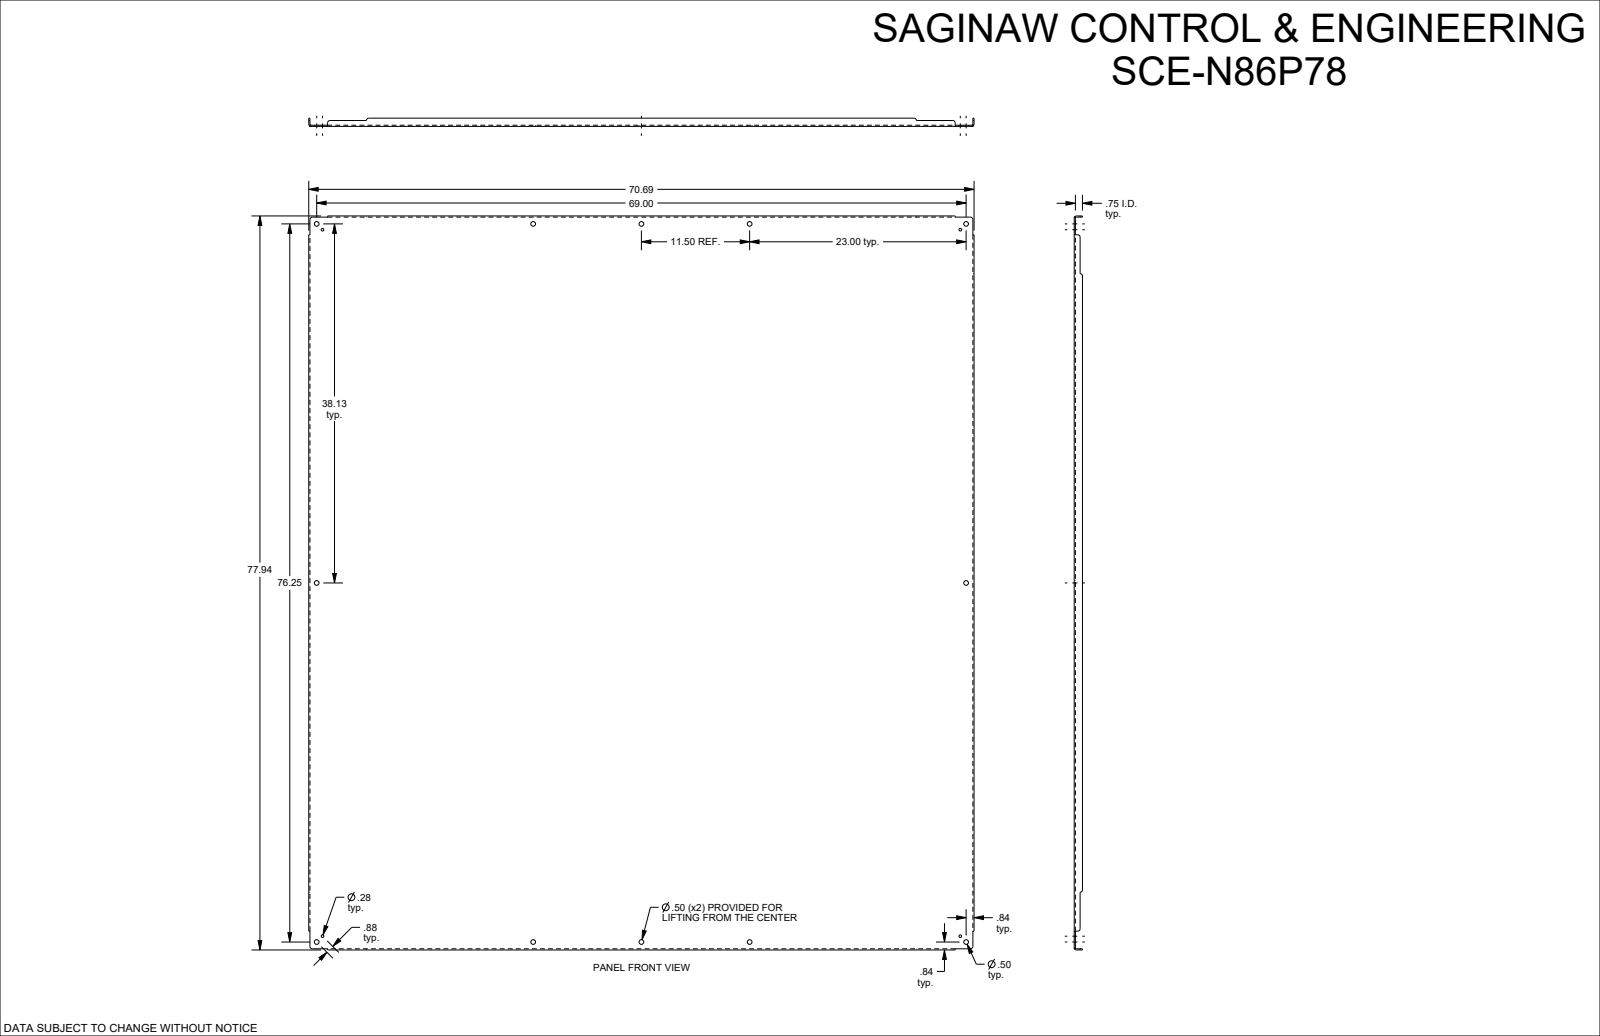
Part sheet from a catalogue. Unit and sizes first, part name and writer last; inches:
Units: inches
Overall size (bounding box): 77.938 × 70.688 × 0.875
Round holes (diameter × count): ⌀0.5 ×12, ⌀0.281 ×4
Partial cylindrical surfaces — rounded edges, fillets, slot ends (radius × count): R0.25 ×13, R0.112 ×4, R0.237 ×4
Main face-to-face distances: 0.125, 70.563, 0.125, 77.813, 70.438, 70.687, 77.687, 77.938, 0.75, 0.875
Hole centre spacings: 23, 79.644, 76.25, 0.875, 11.5, 22.39, 33.887, 34.5
Volume: 710.8 in³ · Surface area: 11 412 in²
Bodies: 1 solid, 130 faces (46 planar, 60 cylindrical, 24 other)
Part name (STEP PRODUCT): SCE-N86P78
STEP written by: SolidWorks 2023 (AUTOMOTIVE_DESIGN)
